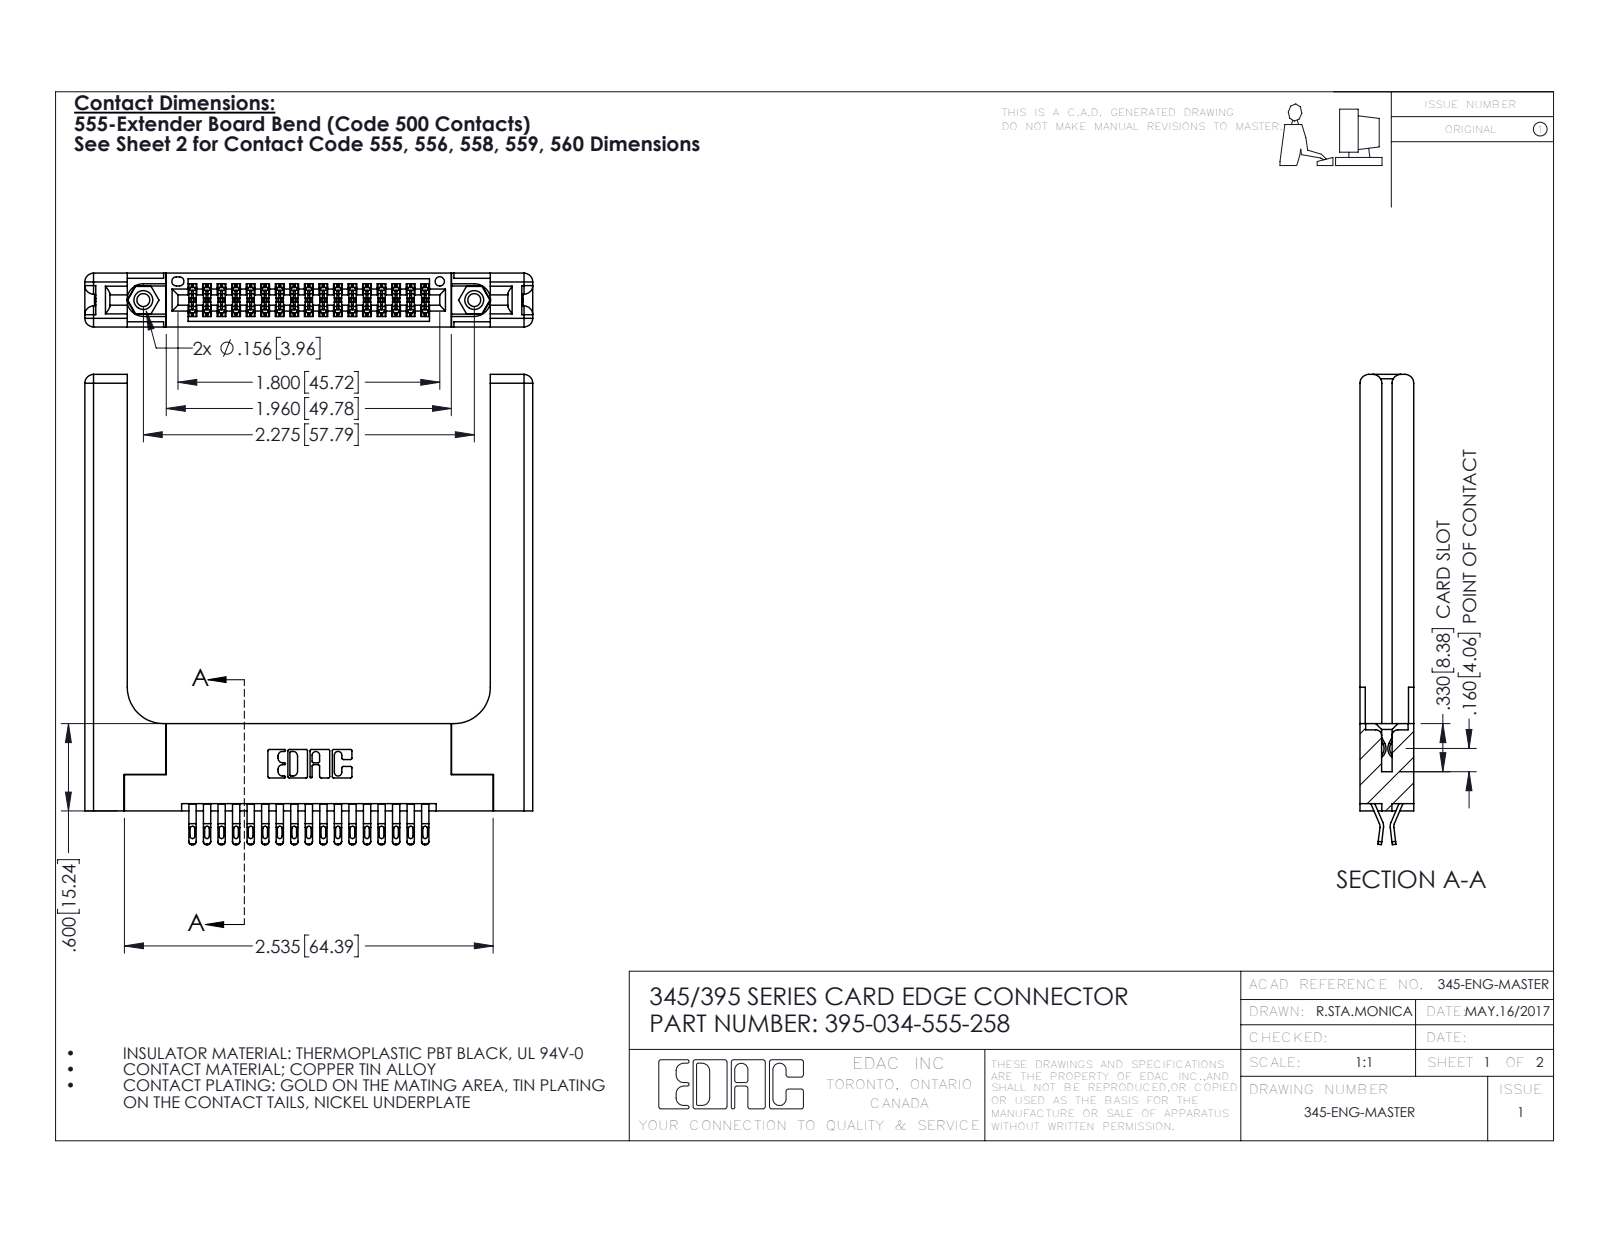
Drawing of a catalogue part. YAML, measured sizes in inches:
part_name: "345 Part_Flush Mounting Lugs - 0.156 Dia-TH; 345-292-001_555 Tail; 345-250-001_345-250-001-102; 345-220-058_345-220-058 (+1 more)"
step_written_by: "SolidWorks 2016 (CONFIG_CONTROL_DESIGN)"
units: inches
bodies: {solids: 39, faces: 2286, planar: 1282, cylindrical: 944, other: 60}
overall_size: [3.232, 3.079, 0.37]
volume: 0.973
surface_area: 24.72
round_holes:
  - {diameter: 0.089, count: 2}
  - {diameter: 0.125, count: 2}
  - {diameter: 0.156, count: 2}
  - {diameter: 0.064, count: 1}
round_bosses_or_shafts:
  - {diameter: 0.155, count: 2}
partial_cylinders:
  - {radius: 0.016, count: 85}
  - {radius: 0.02, count: 68}
  - {radius: 0.006, count: 51}
  - {radius: 0.01, count: 22}
  - {radius: 0.06, count: 16}
  - {radius: 0.007, count: 6}
  - {radius: 0.031, count: 6}
  - {radius: 0.026, count: 3}
face_to_face_distances: [0.37, 0.072, 0.298, 0.148, 0.15, 0.077, 0.2, 0.22, 0.025, 0.225]
hole_center_spacings: [0.27, 2.041, 2.275]
